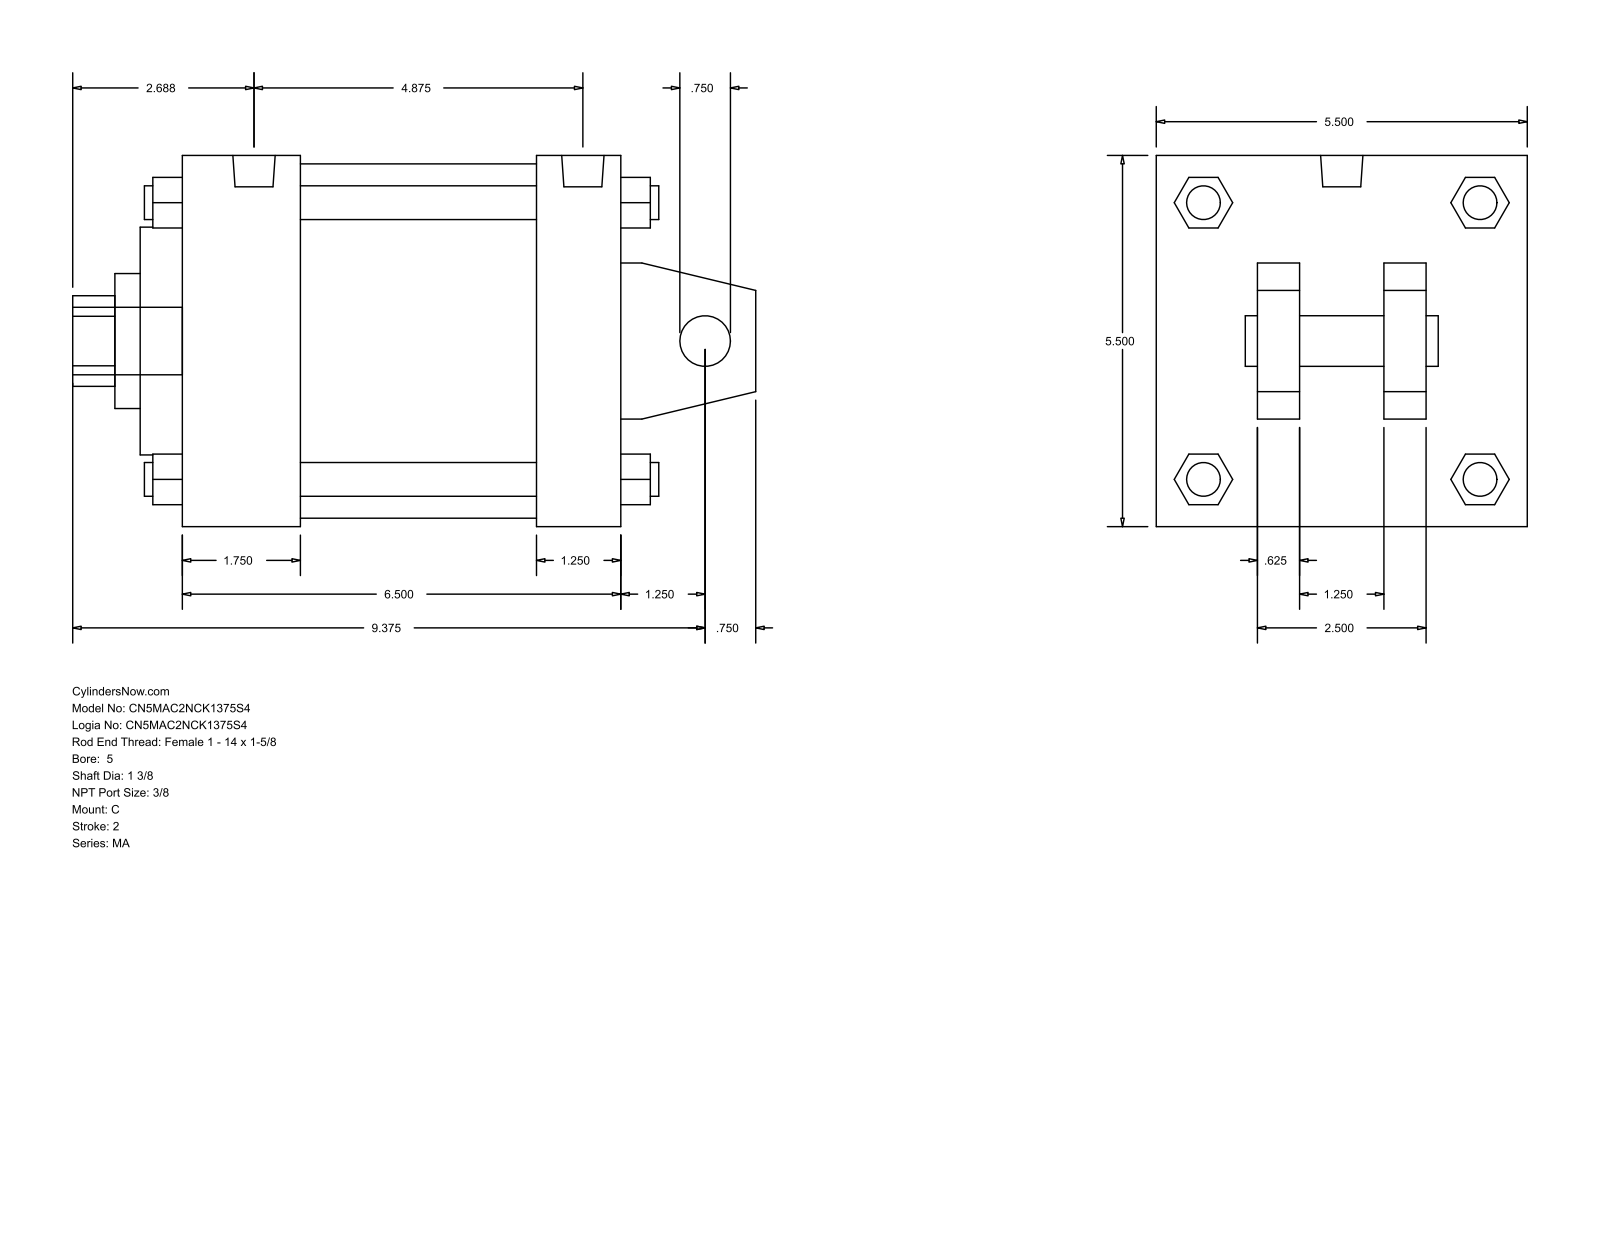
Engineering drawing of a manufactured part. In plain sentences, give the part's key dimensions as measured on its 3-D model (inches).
The part is named "MA_C__0500_1.375". Its 3-D file was written by "GSSL Pune (CONFIG_CONTROL_DESIGN)". It is 0 solids with 141 faces: 109 planar, 32 cylindrical and 0 other. Overall it measures 10.125 by 5.5 by 5.5 inches. Round holes: 1 of diameter 0.75, 1 of diameter 1.375, 1 of diameter 2, 1 of diameter 3.375, 1 of diameter 5.25. Round bosses or shafts: 4 of diameter 0.5, 4 of diameter 0.437, 2 of diameter 0.627, 1 of diameter 1. Partial cylindrical surfaces (rounded edges, fillets, slot ends): 1 of radius 0.672. The main face-to-face distances are 5.5, 6.5, 0.625, 1.25, 5.25, 1.75, 3.5, 4.75, 1.5, 4.
